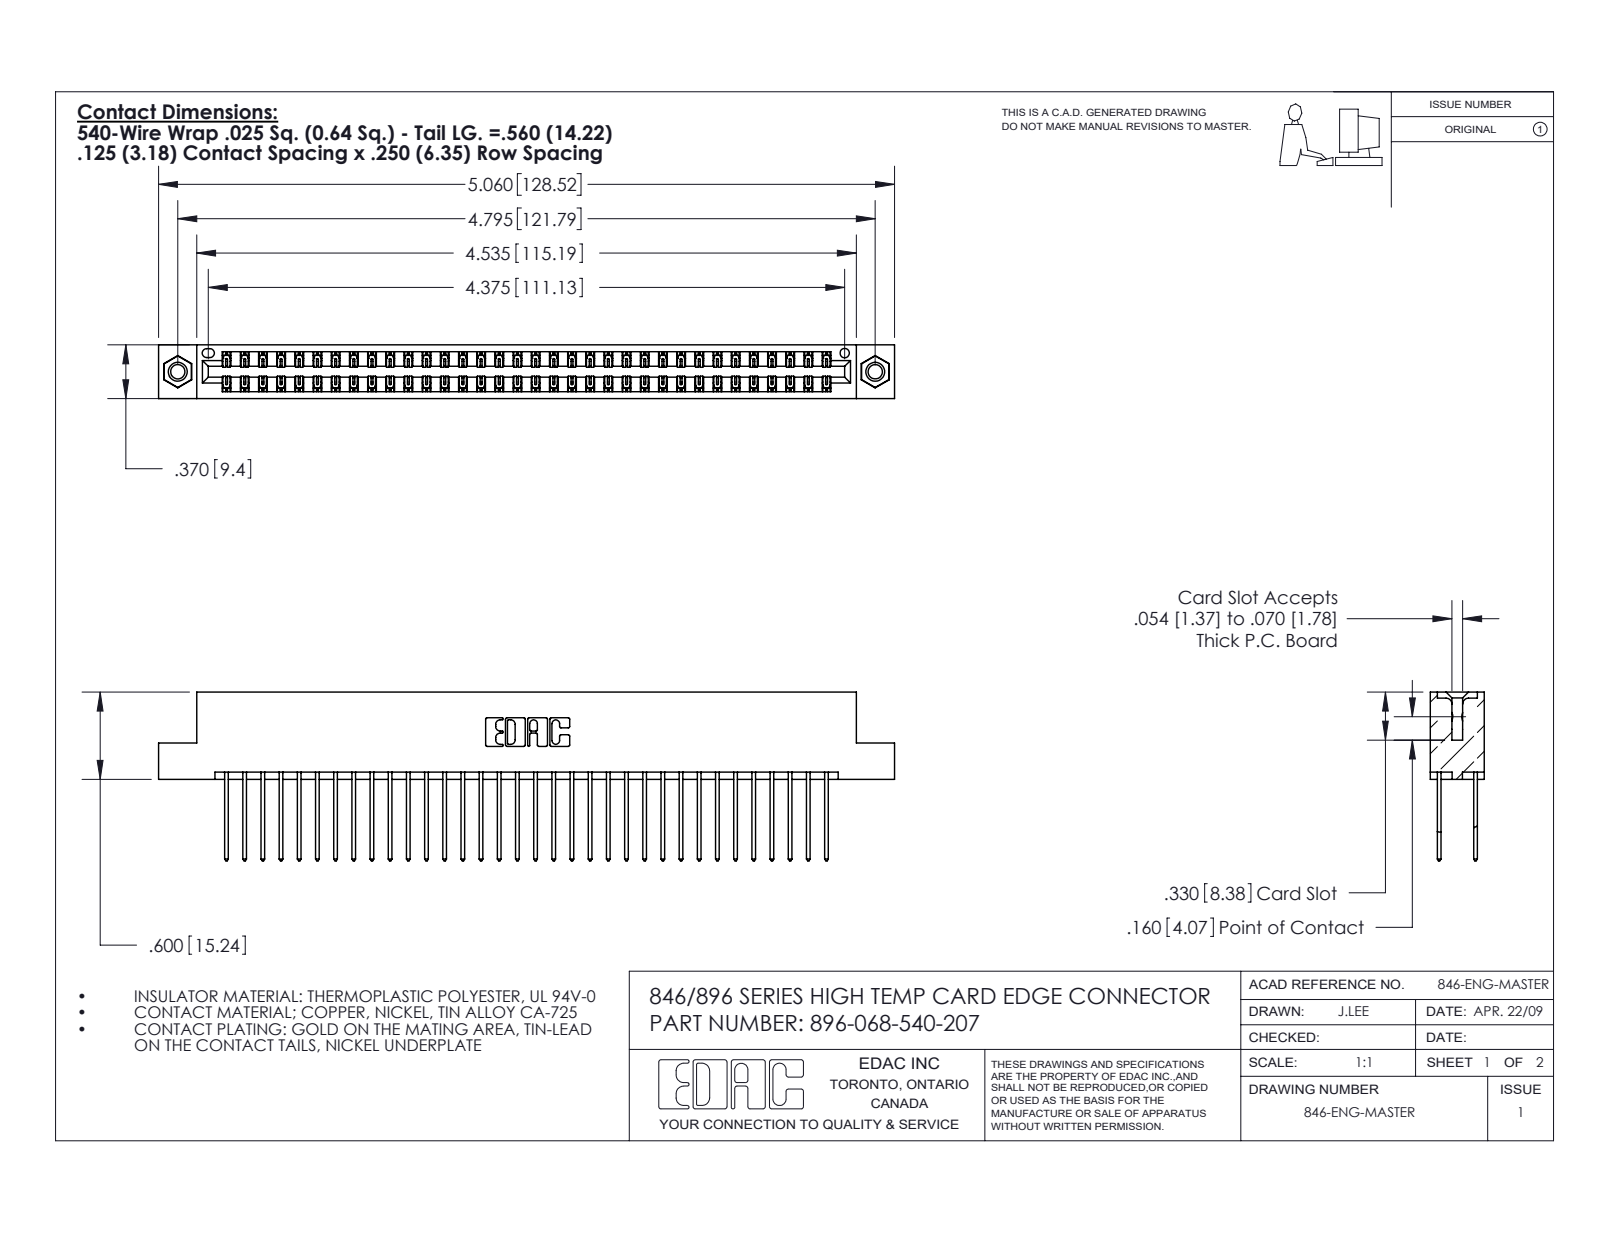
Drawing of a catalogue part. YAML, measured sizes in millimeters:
part_name: "345-292-001_345-293-140; 346 Part_Flush Mounting Lugs - 0.156 Dia-TI; 396-068-540-207; 345-250-001_345-250-005-103"
step_written_by: "SolidWorks 2016 (CONFIG_CONTROL_DESIGN)"
units: millimeters
bodies: {solids: 71, faces: 3718, planar: 2488, cylindrical: 1214, other: 16}
overall_size: [128.5, 29.5, 9.4]
volume: 12700
surface_area: 18610
round_holes:
  - {diameter: 2.5, count: 2}
  - {diameter: 3.2, count: 2}
  - {diameter: 4, count: 2}
  - {diameter: 1.6, count: 1}
round_bosses_or_shafts:
  - {diameter: 3.9, count: 2}
partial_cylinders:
  - {radius: 0.2, count: 102}
  - {radius: 0.3, count: 68}
  - {radius: 0.3, count: 22}
  - {radius: 0.2, count: 6}
  - {radius: 0.8, count: 6}
  - {radius: 0.7, count: 3}
  - {radius: 0.4, count: 2}
  - {radius: 0.6, count: 2}
face_to_face_distances: [1.2, 8.2, 6.4, 1.8, 7.6, 0.6, 9.4, 7, 3.8, 5.6]
hole_center_spacings: [6.2, 116.5, 121.8]
